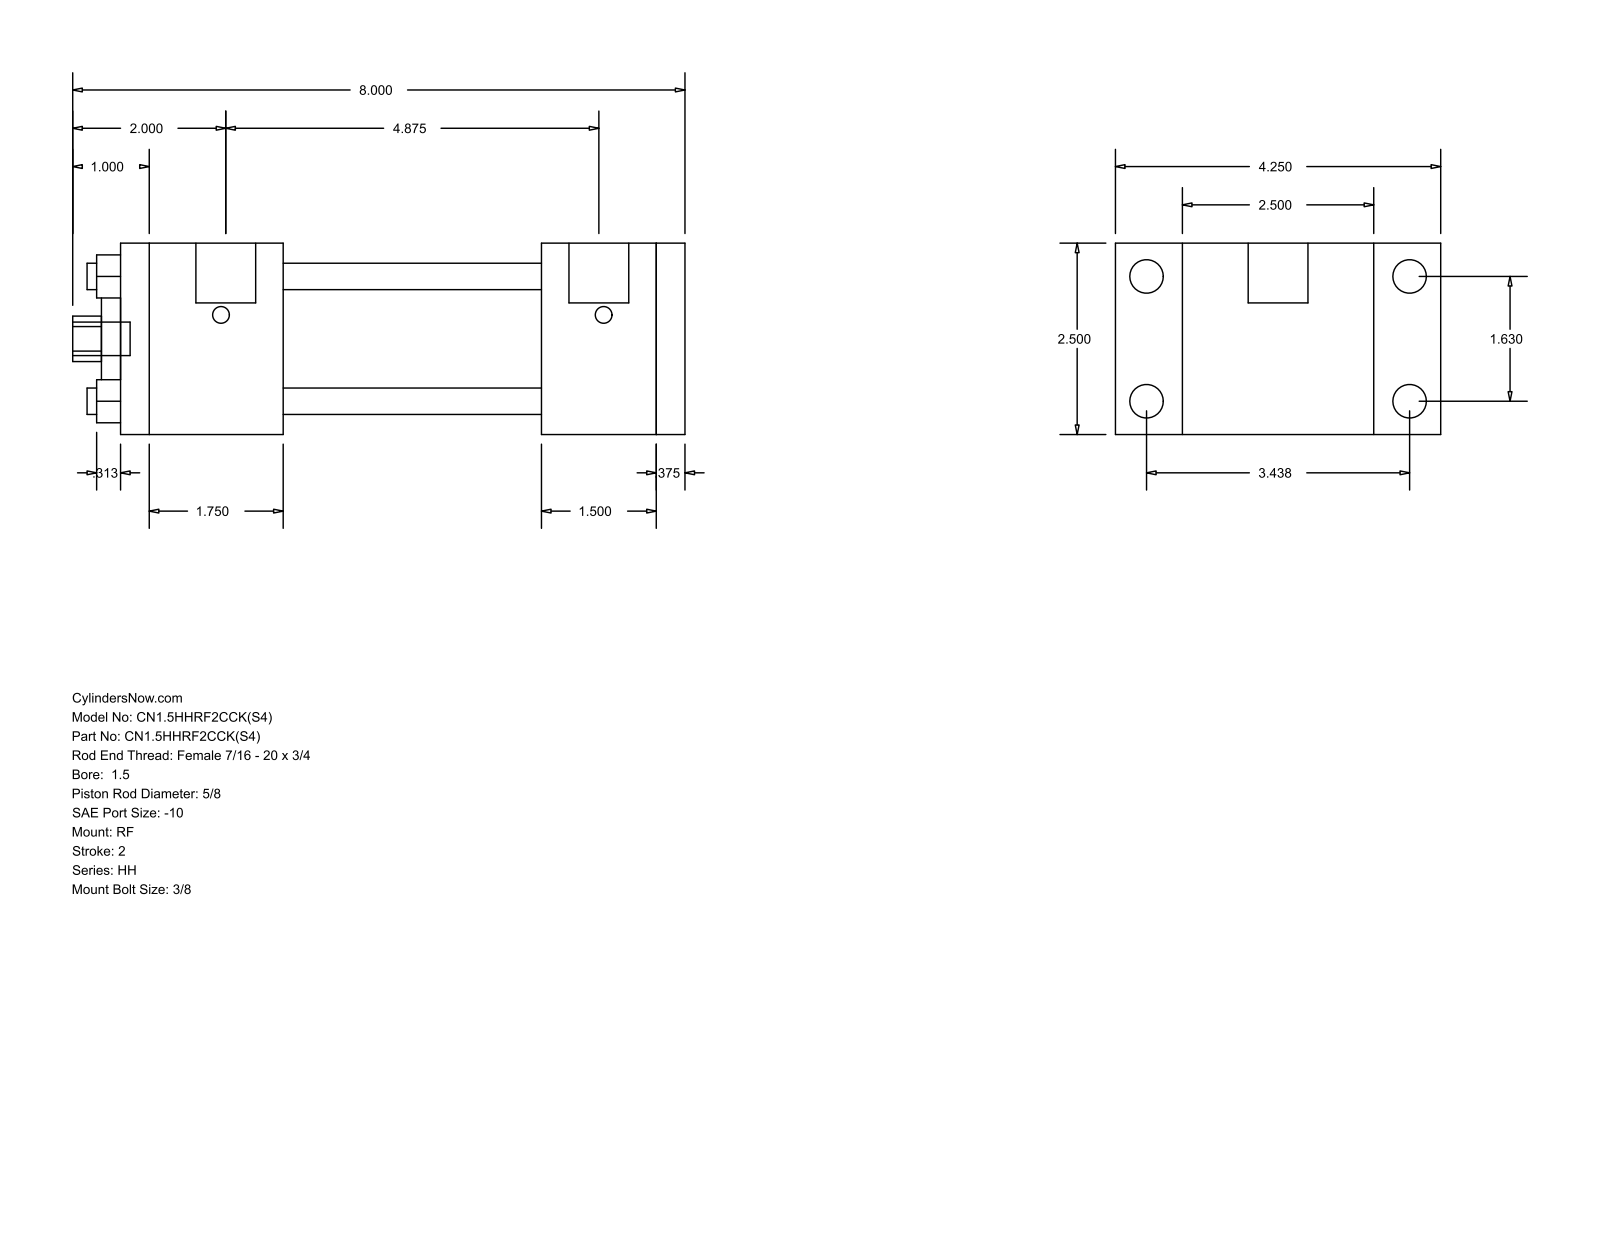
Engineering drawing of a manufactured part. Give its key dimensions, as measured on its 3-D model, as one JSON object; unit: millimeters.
{"part_name": "HH_RF__0150_0.625", "step_written_by": "GSSL Pune (CONFIG_CONTROL_DESIGN)", "units": "millimeters", "bodies": {"solids": 0, "faces": 92, "planar": 64, "cylindrical": 28, "other": 0}, "overall_size": [203.2, 107.95, 63.5], "round_holes": [[8.76, 4], [15.88, 1], [28.57, 1], [44.45, 1]], "round_bosses_or_shafts": [[11.13, 4], [5.56, 4], [19.84, 2], [11.11, 1]], "partial_cylinders_radius": [[7.54, 1]], "face_to_face_distances": [63.5, 187.32, 9.52, 177.8, 47.63, 53.97, 139.69, 85.72, 123.83, 133.35], "hole_center_spacings": [29.27, 41.4, 58.55]}
